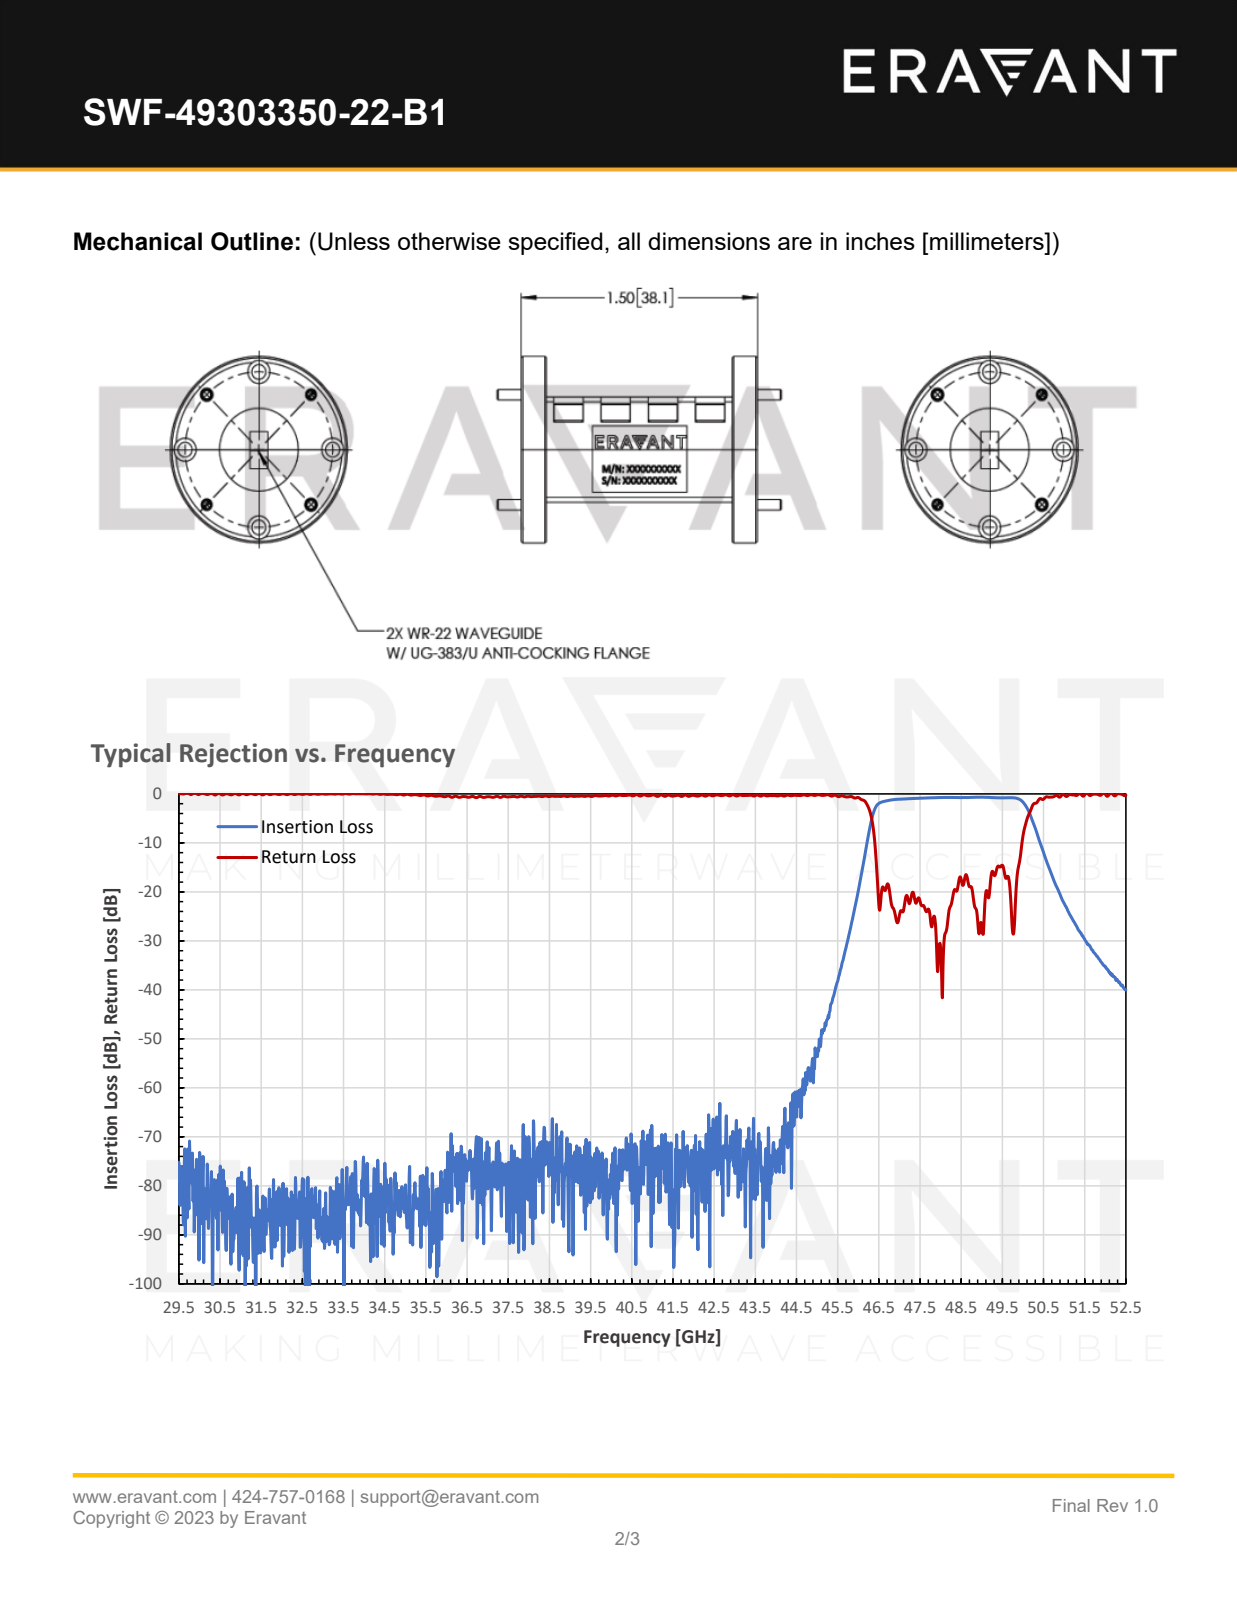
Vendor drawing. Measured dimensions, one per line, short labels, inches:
name: WF-BQ-A
written by: SolidWorks 2021 (CONFIG_CONTROL_DESIGN)
unit: in
bodies: 17 solids, 506 faces (198 planar, 136 cylindrical, 172 other)
size: 1.805 × 1.125 × 1.125
volume: 0.624 in³; area: 9.665 in²
holes: 4× ⌀0.061, 4× ⌀0.067, 4× ⌀0.089, 4× ⌀0.11, 4× ⌀0.14, 1× ⌀1.055
bosses: 8× ⌀0.183, 8× ⌀0.112, 4× ⌀0.096, 4× ⌀0.063, 4× ⌀0.06, 1× ⌀1.125, 1× ⌀0.5
rounds: 8× R0.095
face distances: 0.14, 1.32, 1.18, 1.46, 0.485, 0.635, 0.125, 0.36, 1.48, 0.02
hole spacings: 0.359, 0.866, 0.663, 0.469, 0.4, 0.469, 0.937, 0.938
